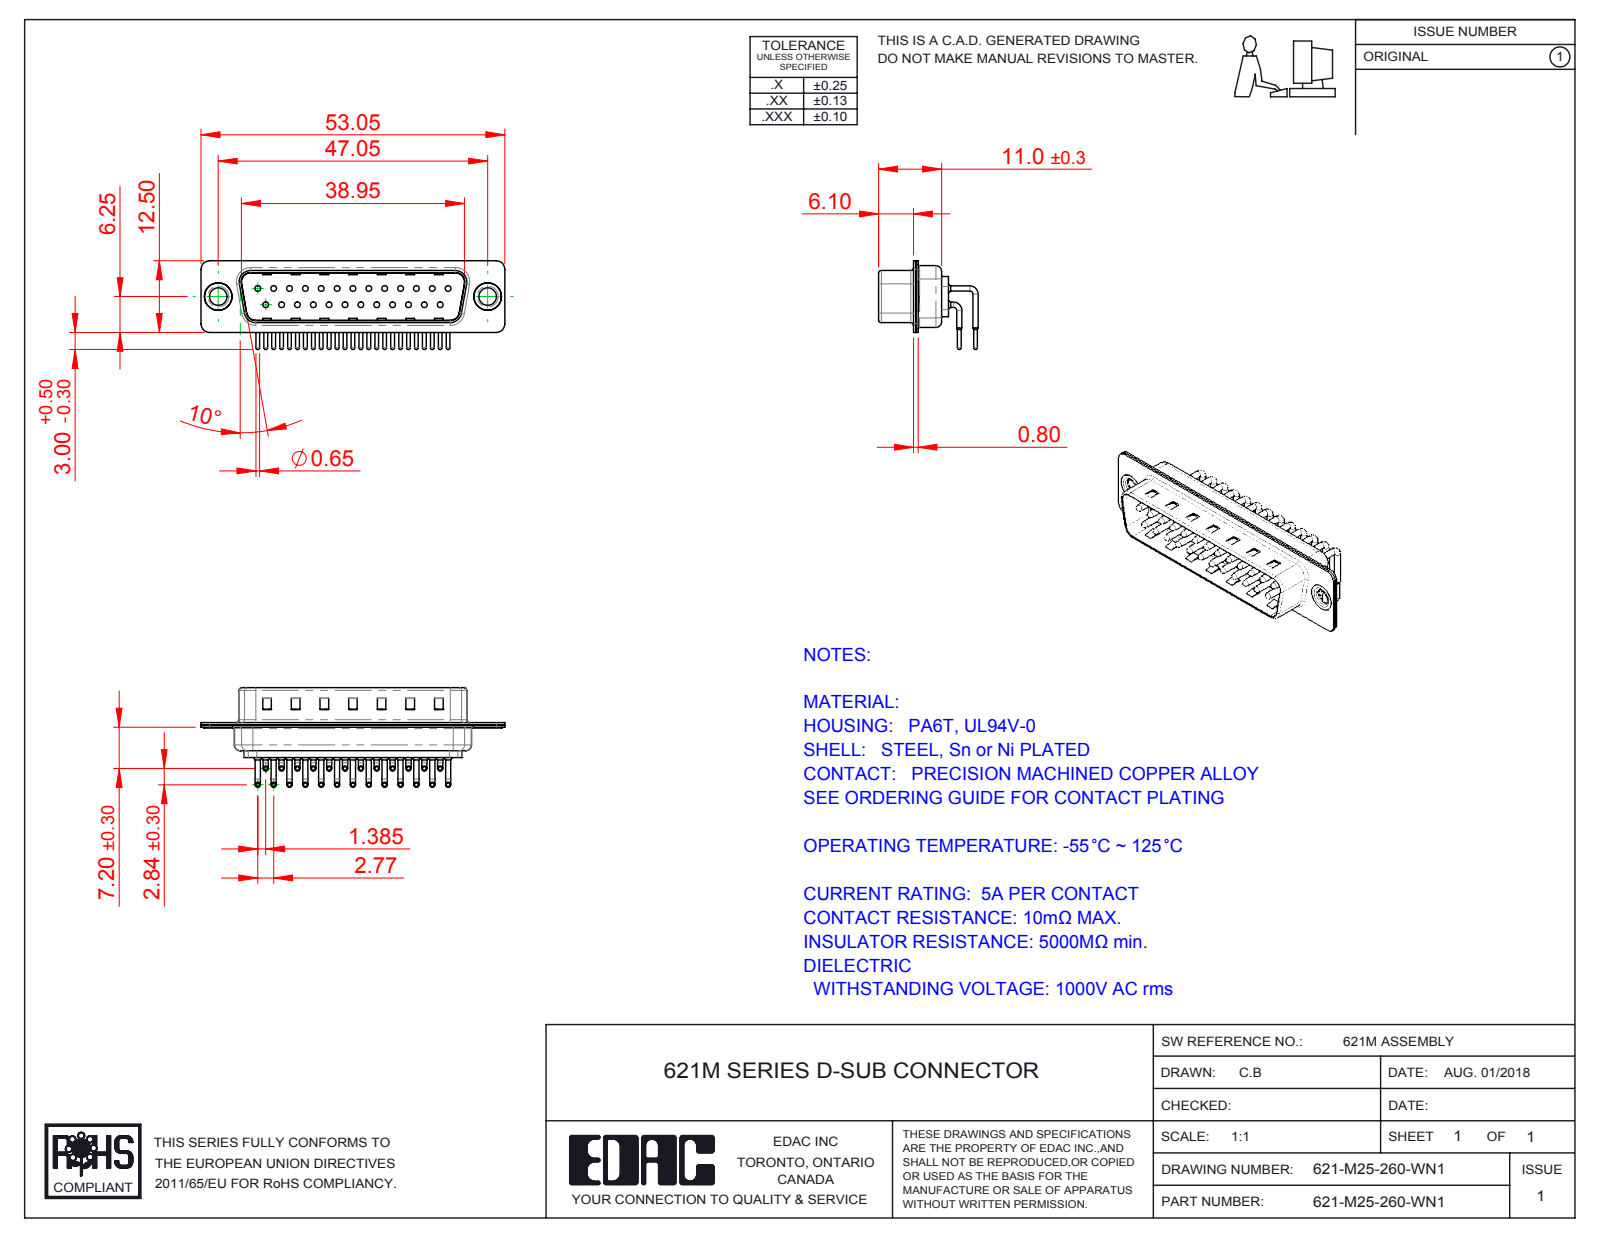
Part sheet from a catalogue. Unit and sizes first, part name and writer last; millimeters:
Units: millimetres
Overall size (bounding box): 53.05 × 17.39 × 15.49
Round holes (diameter × count): ⌀1 ×25, ⌀1.7 ×25, ⌀2 ×25, ⌀3.05 ×2, ⌀4 ×2, ⌀4.8 ×2
Round bosses / shafts (diameter × count): ⌀0.9 ×50, ⌀1.5 ×25, ⌀0.65 ×25, ⌀5 ×2, ⌀4.9 ×2, ⌀3.55 ×2
Partial cylindrical surfaces — rounded edges, fillets, slot ends (radius × count): R1.01 ×25, R1.5 ×16, R2 ×12, R0.5 ×8, R1.6 ×8, R0.25 ×4, R0.6 ×4, R0.65 ×4
Main face-to-face distances: 0.4, 0.85, 9.55, 8.7, 1.25, 10.4, 1.5, 1.9, 0.35, 6.1
Hole centre spacings: 3.16, 8.31, 2.77, 5.54, 11.08, 16.62, 5.03, 5.04
Volume: 2 796 mm³ · Surface area: 7 439 mm²
Bodies: 30 solids, 3100 faces (1771 planar, 1021 cylindrical, 308 other)
Part name (STEP PRODUCT): 621M Housing_25 Contacts; 621M Shell Front_25 Contacts; 621M Shell Rear_25 Contacts; 621-M25-260-WN1 (+3 more)
STEP written by: SolidWorks 2016 (CONFIG_CONTROL_DESIGN)
